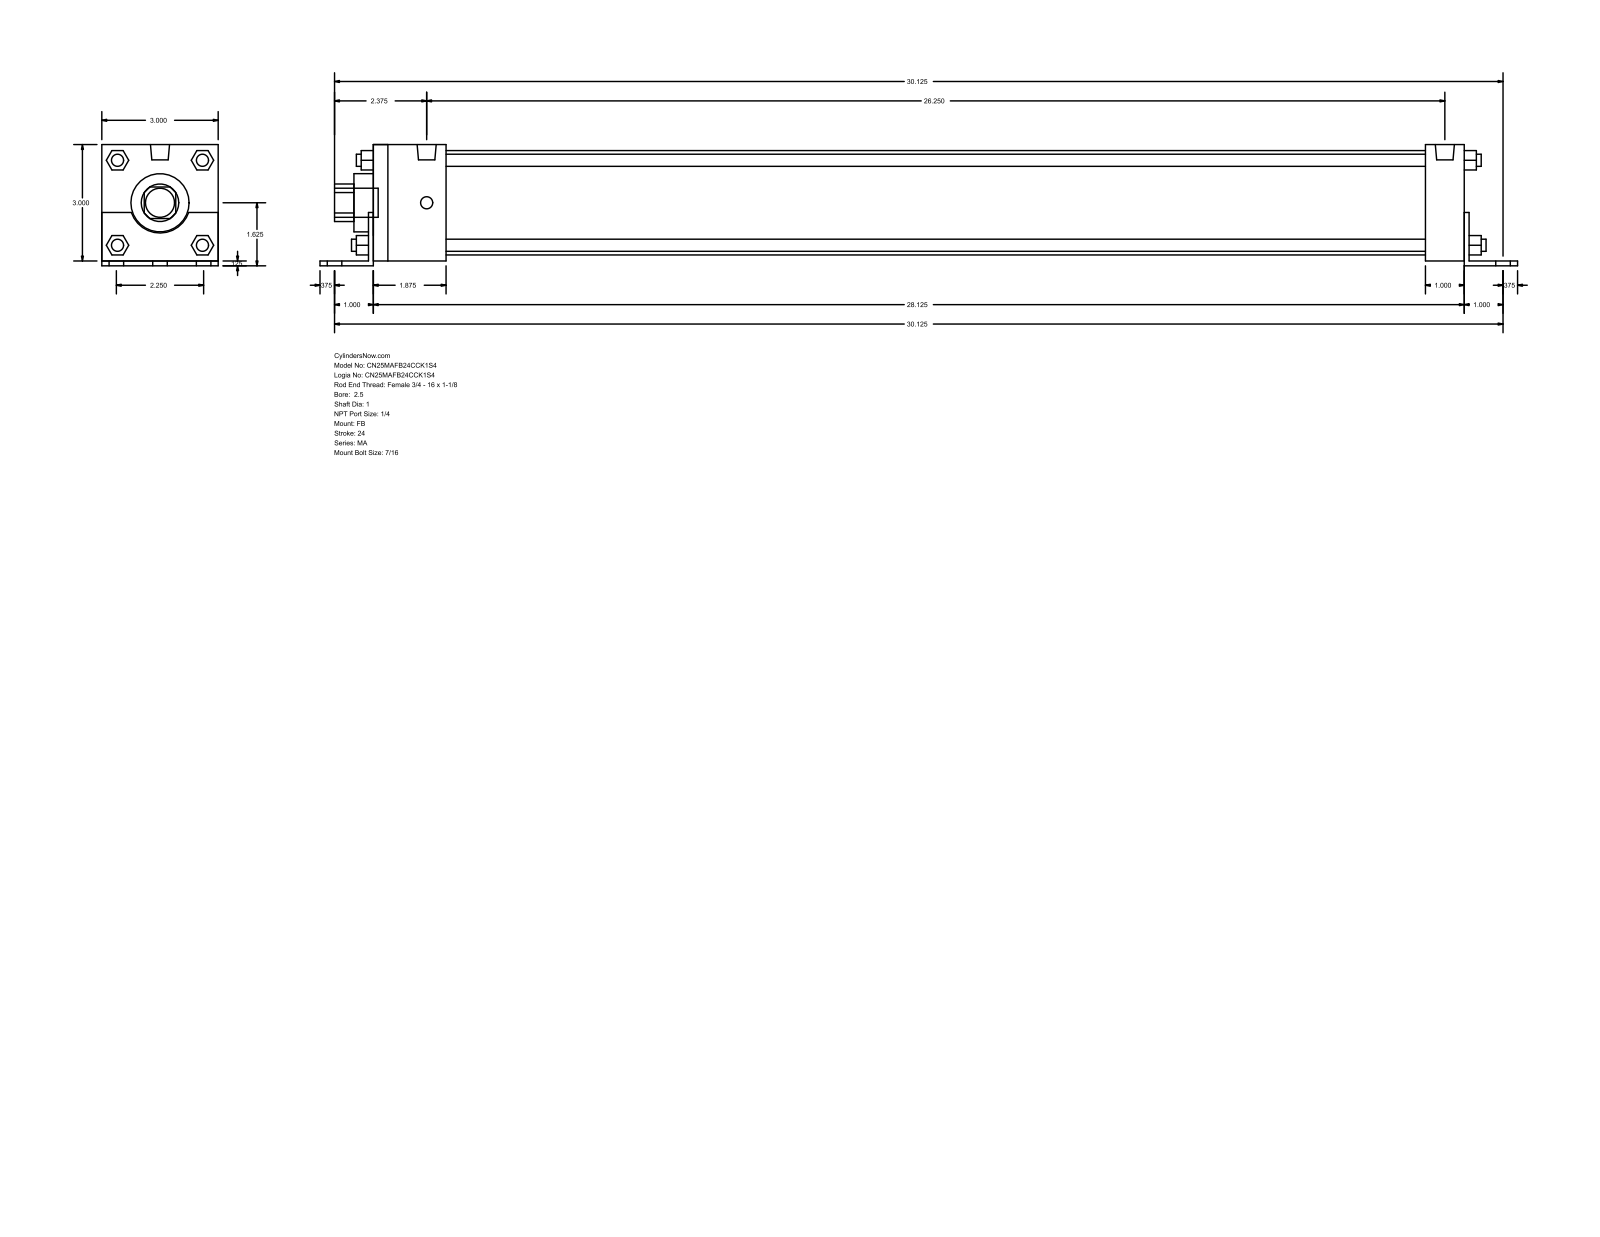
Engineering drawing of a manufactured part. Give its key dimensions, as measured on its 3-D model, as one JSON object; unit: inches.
{"part_name": "MA_FB__0250_1", "step_written_by": "GSSL Pune (CONFIG_CONTROL_DESIGN)", "units": "inches", "bodies": {"solids": 0, "faces": 140, "planar": 105, "cylindrical": 35, "other": 0}, "overall_size": [30.875, 3.125, 3], "round_holes": [[1, 1], [1.5, 1], [2.69, 1]], "round_bosses_or_shafts": [[0.313, 8], [0.437, 6], [0.492, 2], [0.75, 1]], "partial_cylinders_radius": [[0.484, 1], [0.78, 1]], "face_to_face_distances": [3, 0.125, 3.125, 28.125, 0.125, 0.5, 28.25, 1.125, 1.875, 26.25]}
